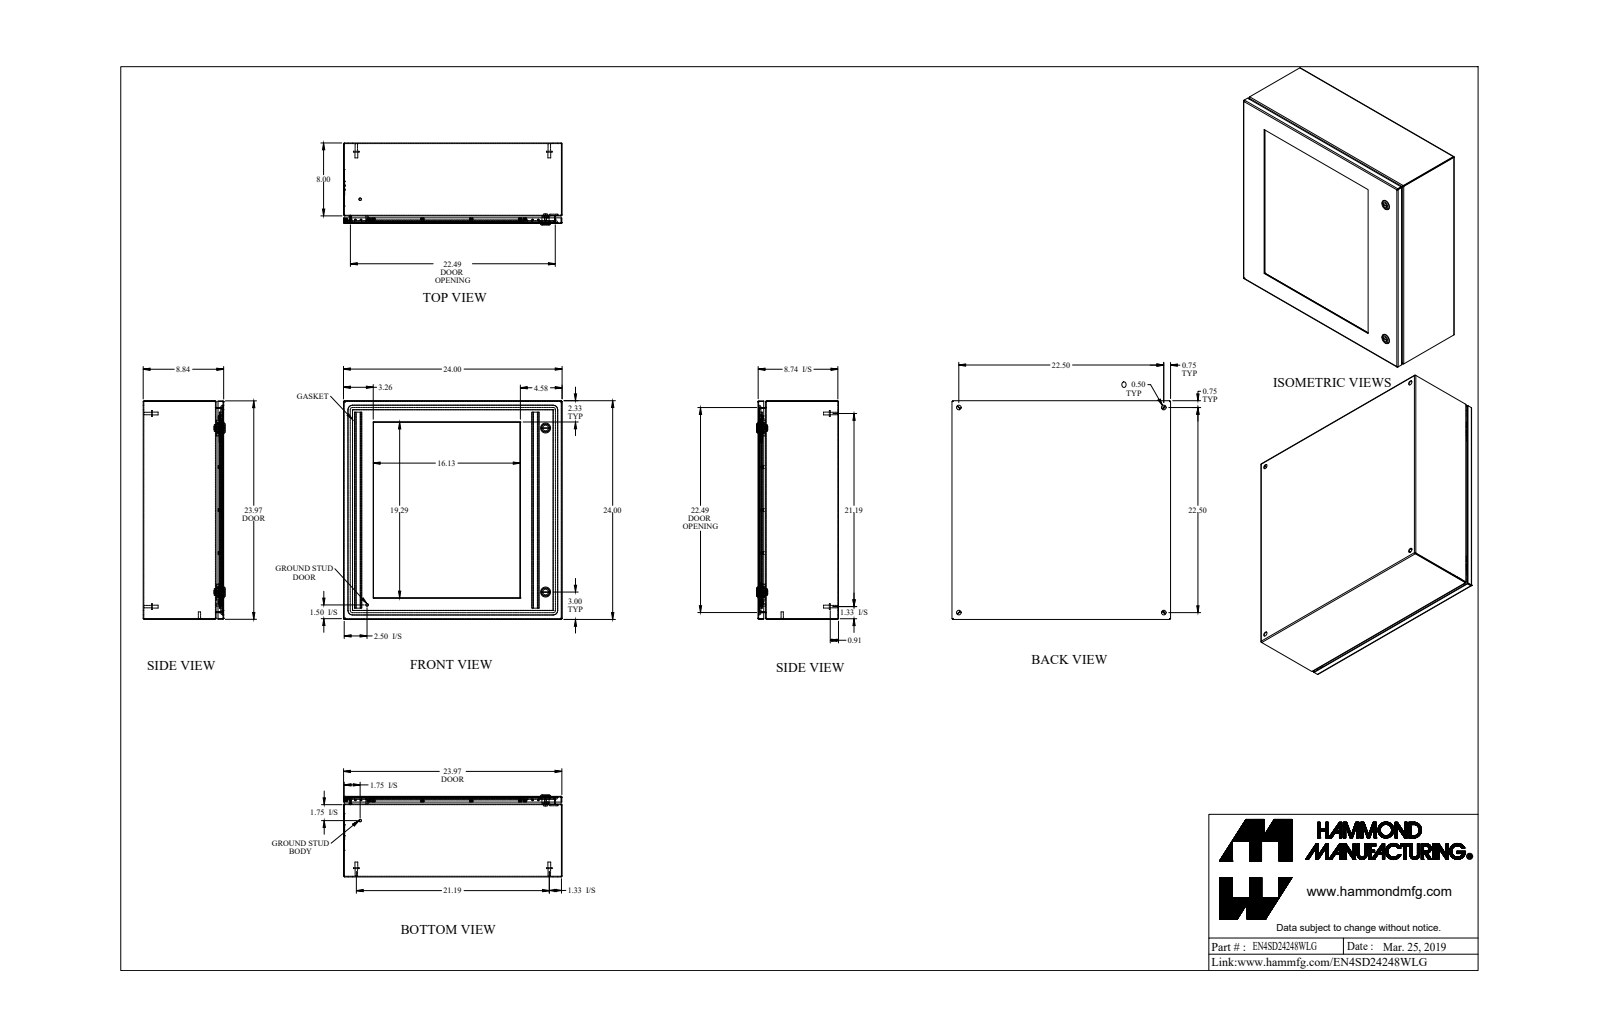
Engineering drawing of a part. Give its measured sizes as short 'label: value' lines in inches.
name: EN4SD24248WLG_Default
written by: SolidWorks 2019 (CONFIG_CONTROL_DESIGN)
unit: in
bodies: 72 solids, 1482 faces (763 planar, 453 cylindrical, 266 other)
size: 24 × 24 × 8.997
volume: 230.8 in³; area: 4 884 in²
holes: 18× ⌀0.13, 18× ⌀0.25, 4× ⌀0.5, 2× ⌀0.232, 2× ⌀0.625, 2× ⌀0.785, 1× ⌀0.172, 1× ⌀0.24, 1× ⌀0.242
bosses: 19× ⌀0.226, 18× ⌀0.368, 18× ⌀0.164, 4× ⌀0.625, 4× ⌀0.313, 4× ⌀0.27, 2× ⌀1.1, 2× ⌀0.525
rounds: 20× R0.036, 20× R0.108, 12× R0.043, 12× R0.081, 12× R0.125, 12× R0.382, 8× R19.003, 4× R0.006
face distances: 0.072, 8.765, 23.928, 8.693, 8.443, 0.25, 8.515, 23.856, 24, 0.322
hole spacings: 4.719, 17.781, 14.156, 18.875, 19.57, 21.03, 5.372, 5.372
